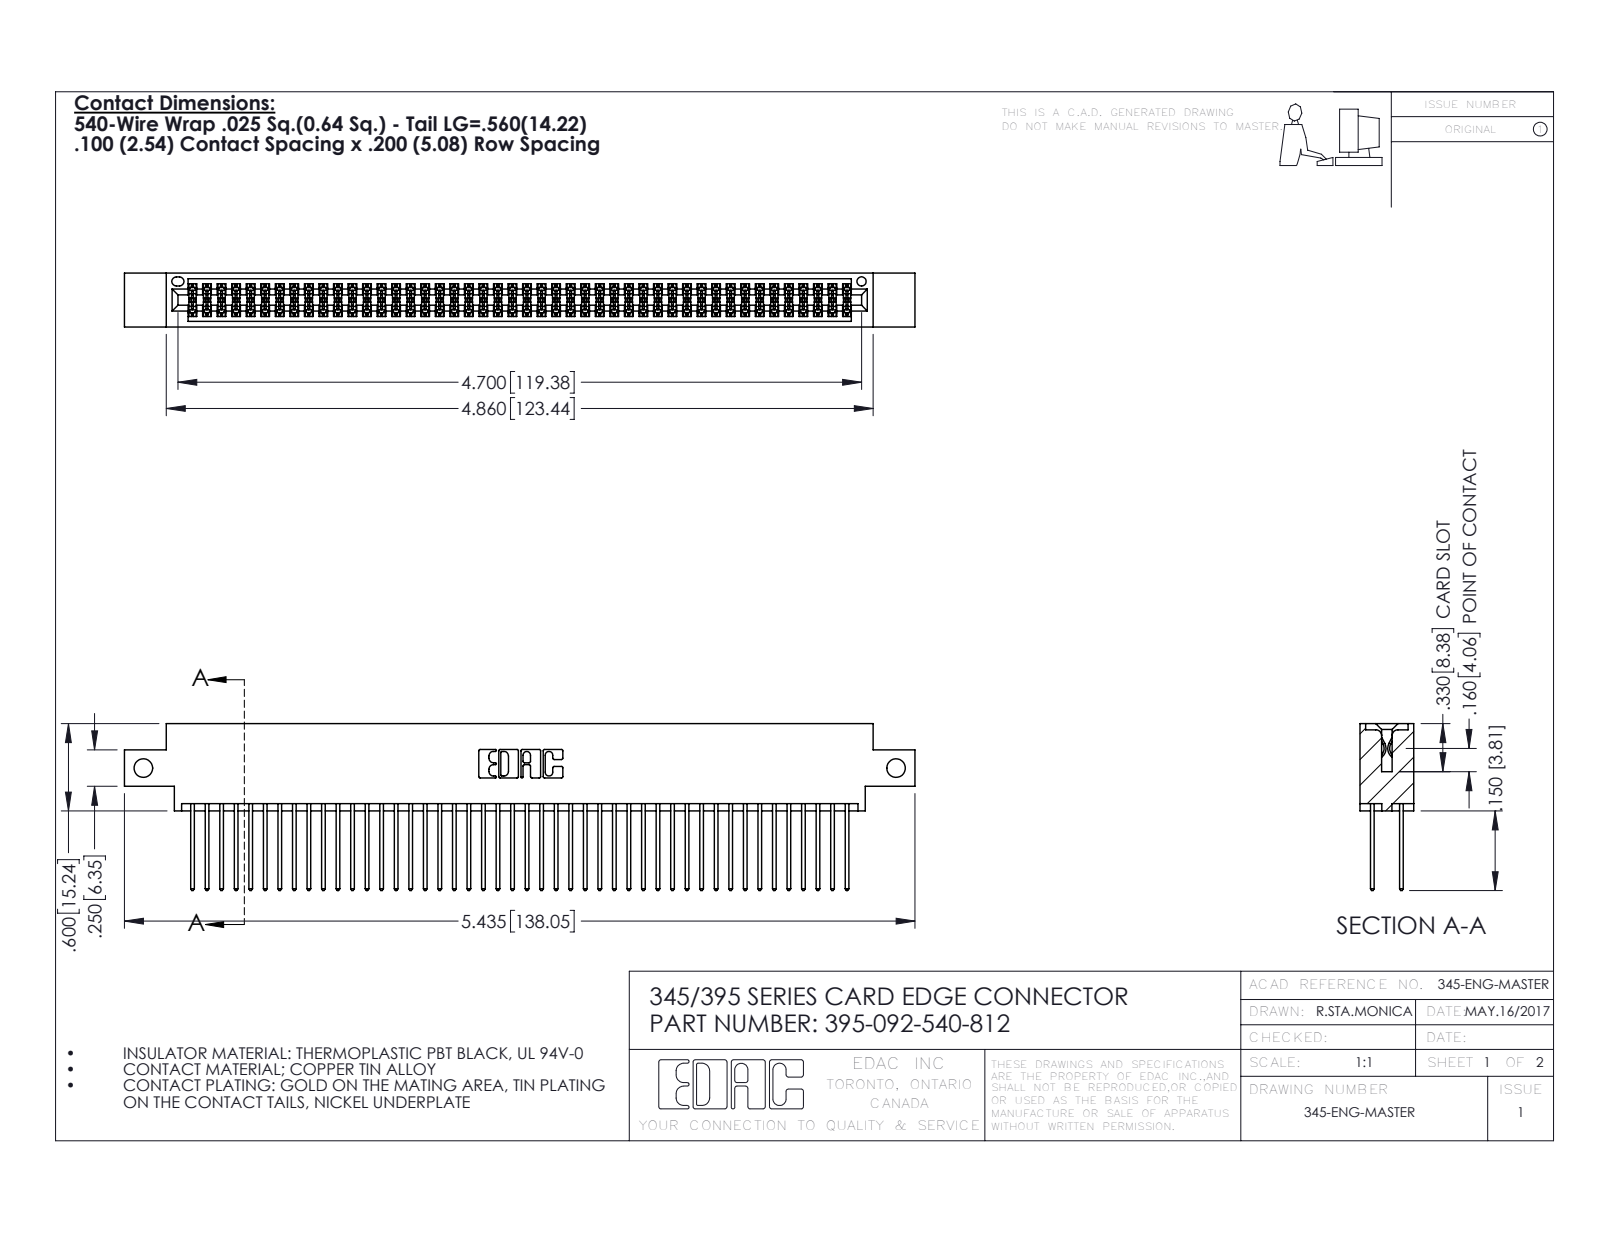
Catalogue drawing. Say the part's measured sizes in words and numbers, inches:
The part is named "395-092-540-812; 345-292-001_345-293-140; 345 Part_0.170 Offset - Side Mount". Its 3-D file was written by "SolidWorks 2016 (CONFIG_CONTROL_DESIGN)". It is 93 solids with 4730 faces: 3120 planar, 1610 cylindrical and 0 other. Overall it measures 5.435 by 1.147 by 0.37 inches. Its volume is 0.83 cubic inches and its surface area 33.79 square inches. Round holes: 2 of diameter 0.128, 1 of diameter 0.064. Partial cylindrical surfaces (rounded edges, fillets, slot ends): 138 of radius 0.006, 92 of radius 0.01, 22 of radius 0.01, 6 of radius 0.007, 6 of radius 0.031, 3 of radius 0.026, 2 of radius 0.014, 2 of radius 0.019. The main face-to-face distances are 0.298, 0.072, 0.2, 0.098, 0.272, 0.025, 0.37, 0.225, 0.175, 0.149. The hole center spacings are 5.175.
